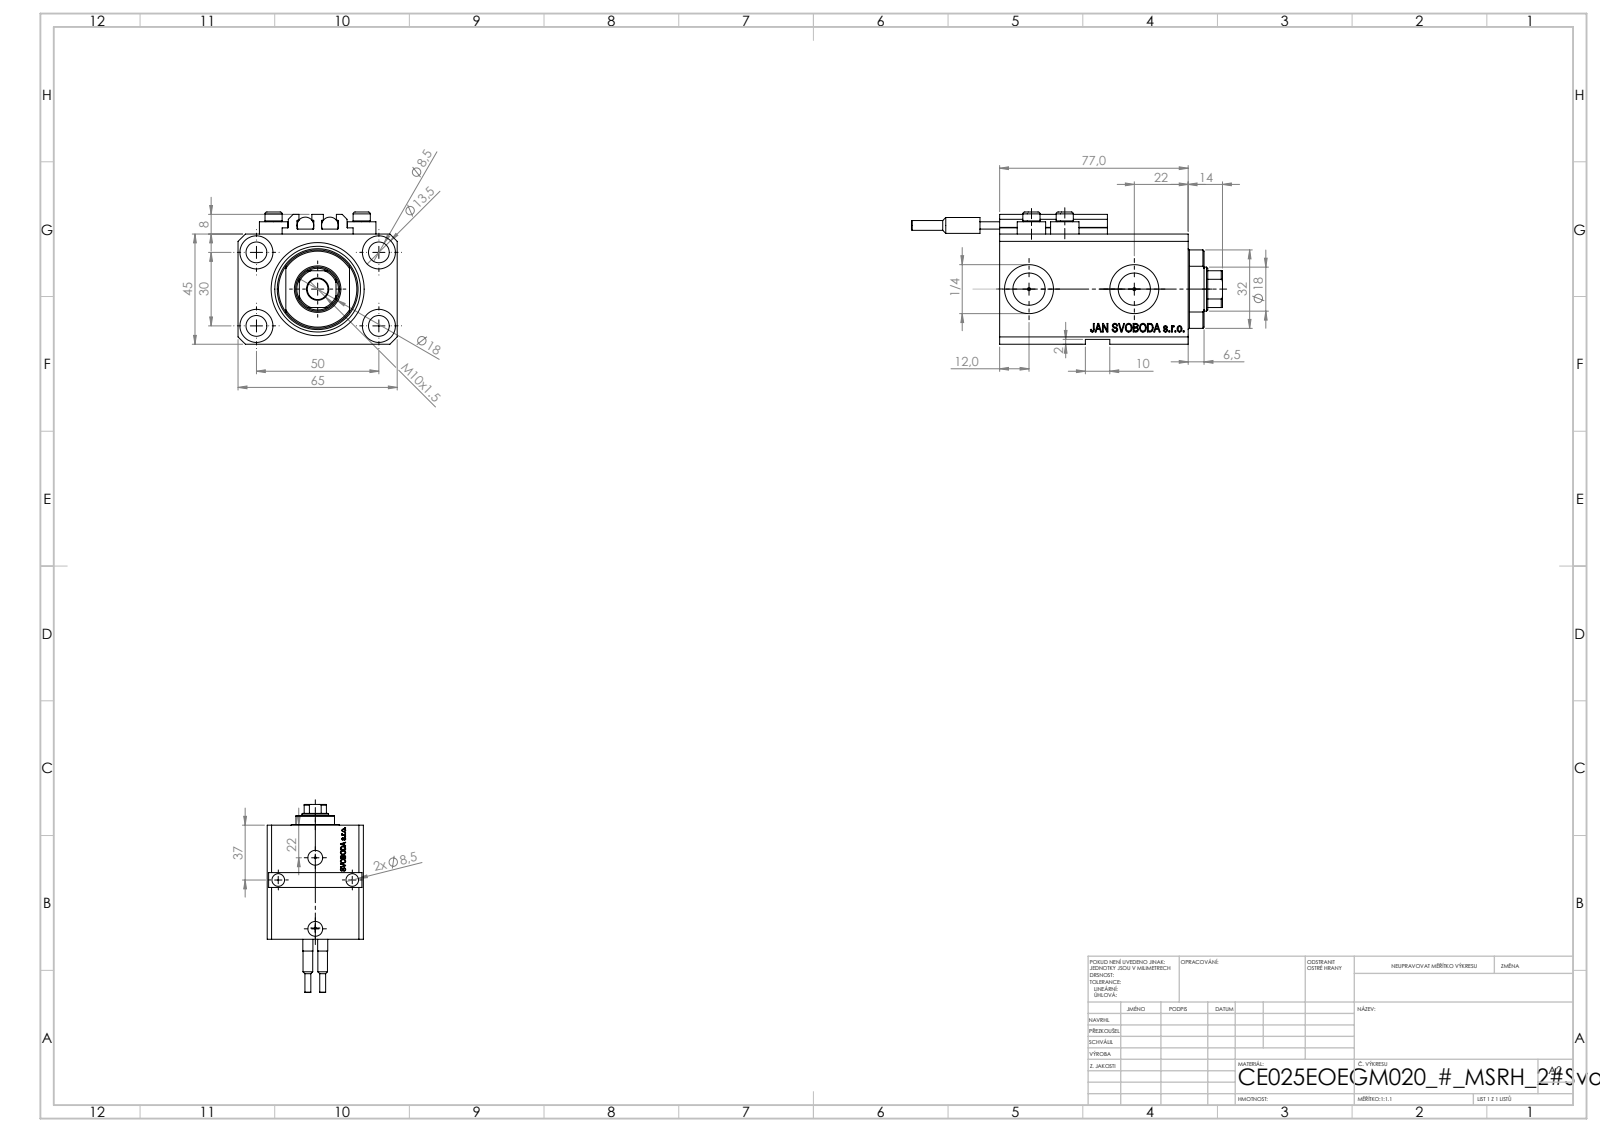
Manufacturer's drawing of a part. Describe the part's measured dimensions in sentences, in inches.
The part is named "V250CE_C_VCP; V250CE_E_Body; ALLEN BOLT V250CE; V250CE_VC_E (+1 more)". Its 3-D file was written by "SolidWorks 2019 (CONFIG_CONTROL_DESIGN)". It is 10 solids with 1119 faces: 543 planar, 138 cylindrical and 438 other. Overall it measures 5 by 2.559 by 2.126 inches. Its volume is 12.41 cubic inches and its surface area 96 square inches. Round holes: 7 of diameter 0.335, 4 of diameter 0.049, 4 of diameter 0.157, 4 of diameter 0.531, 2 of diameter 0.394, 2 of diameter 0.518, 2 of diameter 0.787, 1 of diameter 0.709, 1 of diameter 0.984, 1 of diameter 1.496. Round bosses or shafts: 4 of diameter 0.457, 4 of diameter 0.276, 2 of diameter 0.268, 2 of diameter 0.256, 2 of diameter 0.157. Partial cylindrical surfaces (rounded edges, fillets, slot ends): 10 of radius 0.008, 1 of radius 0.335, 1 of radius 0.63. The main face-to-face distances are 1.772, 2.559, 2.48, 0.079, 0.551, 0.118, 3.031, 1.85, 0.197, 0.272. The hole center spacings are 1.148, 1.969, 0.535, 0.595, 0.741, 0.747, 1.032, 1.048.
